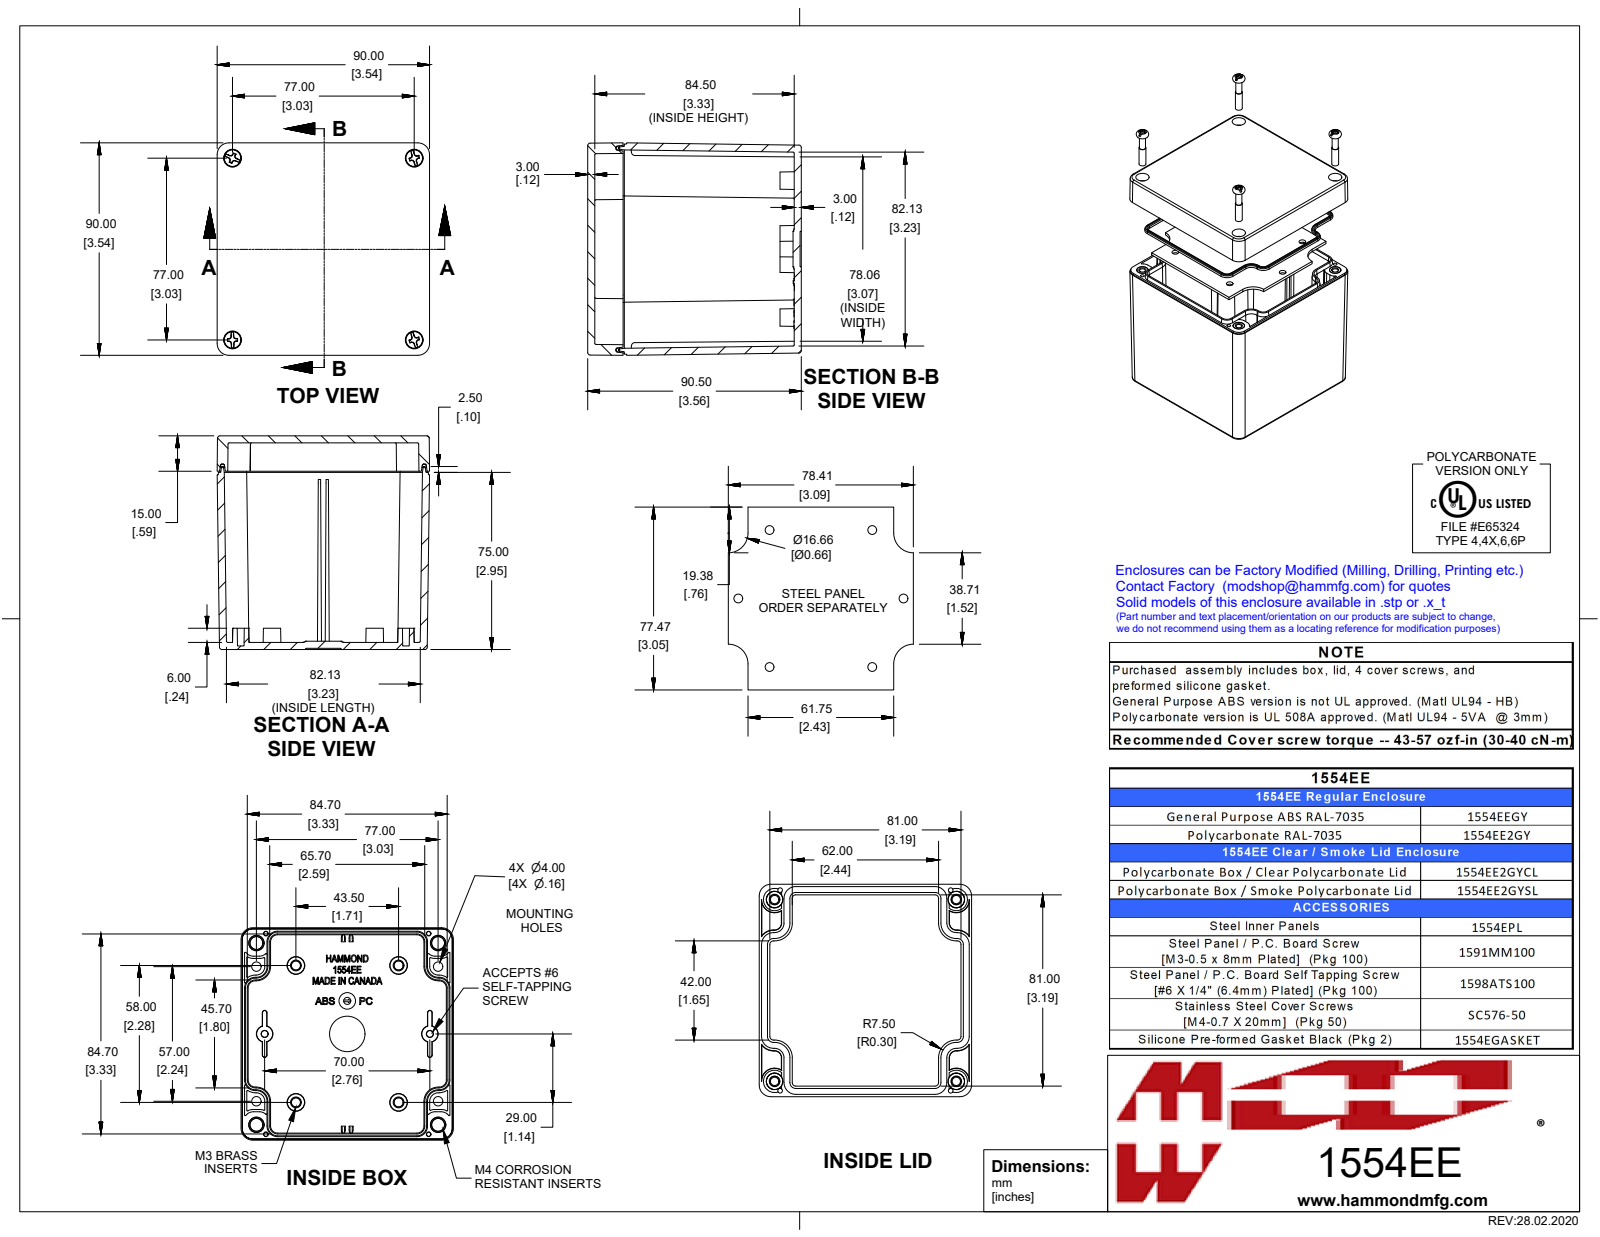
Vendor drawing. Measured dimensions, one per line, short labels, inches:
name: 1554EE2GY
written by: SolidWorks 2019 (AUTOMOTIVE_DESIGN)
unit: in
bodies: 16 solids, 1813 faces (694 planar, 337 cylindrical, 782 other)
size: 3.563 × 3.543 × 3.543
volume: 10.54 in³; area: 202.9 in²
holes: 5× ⌀0.276, 4× ⌀0.079, 4× ⌀0.097, 4× ⌀0.128, 4× ⌀0.138, 4× ⌀0.147, 2× ⌀0.11, 1× ⌀0.591
bosses: 4× ⌀0.25, 4× ⌀0.218, 4× ⌀0.21, 4× ⌀0.19, 4× ⌀0.154, 4× ⌀0.153, 4× ⌀0.15, 4× ⌀0.135
rounds: 32× R0.02, 8× R0.039, 8× R0.197, 4× R0.187, 4× R0.328, 2× R0.059
face distances: 0.118, 3.445, 0.059, 3.563, 0.354, 3.091, 3.209, 0.064, 0.419, 3.026
hole spacings: 2.341, 2.738, 2.87, 0.181, 0.757, 0.758, 0.776, 0.776
